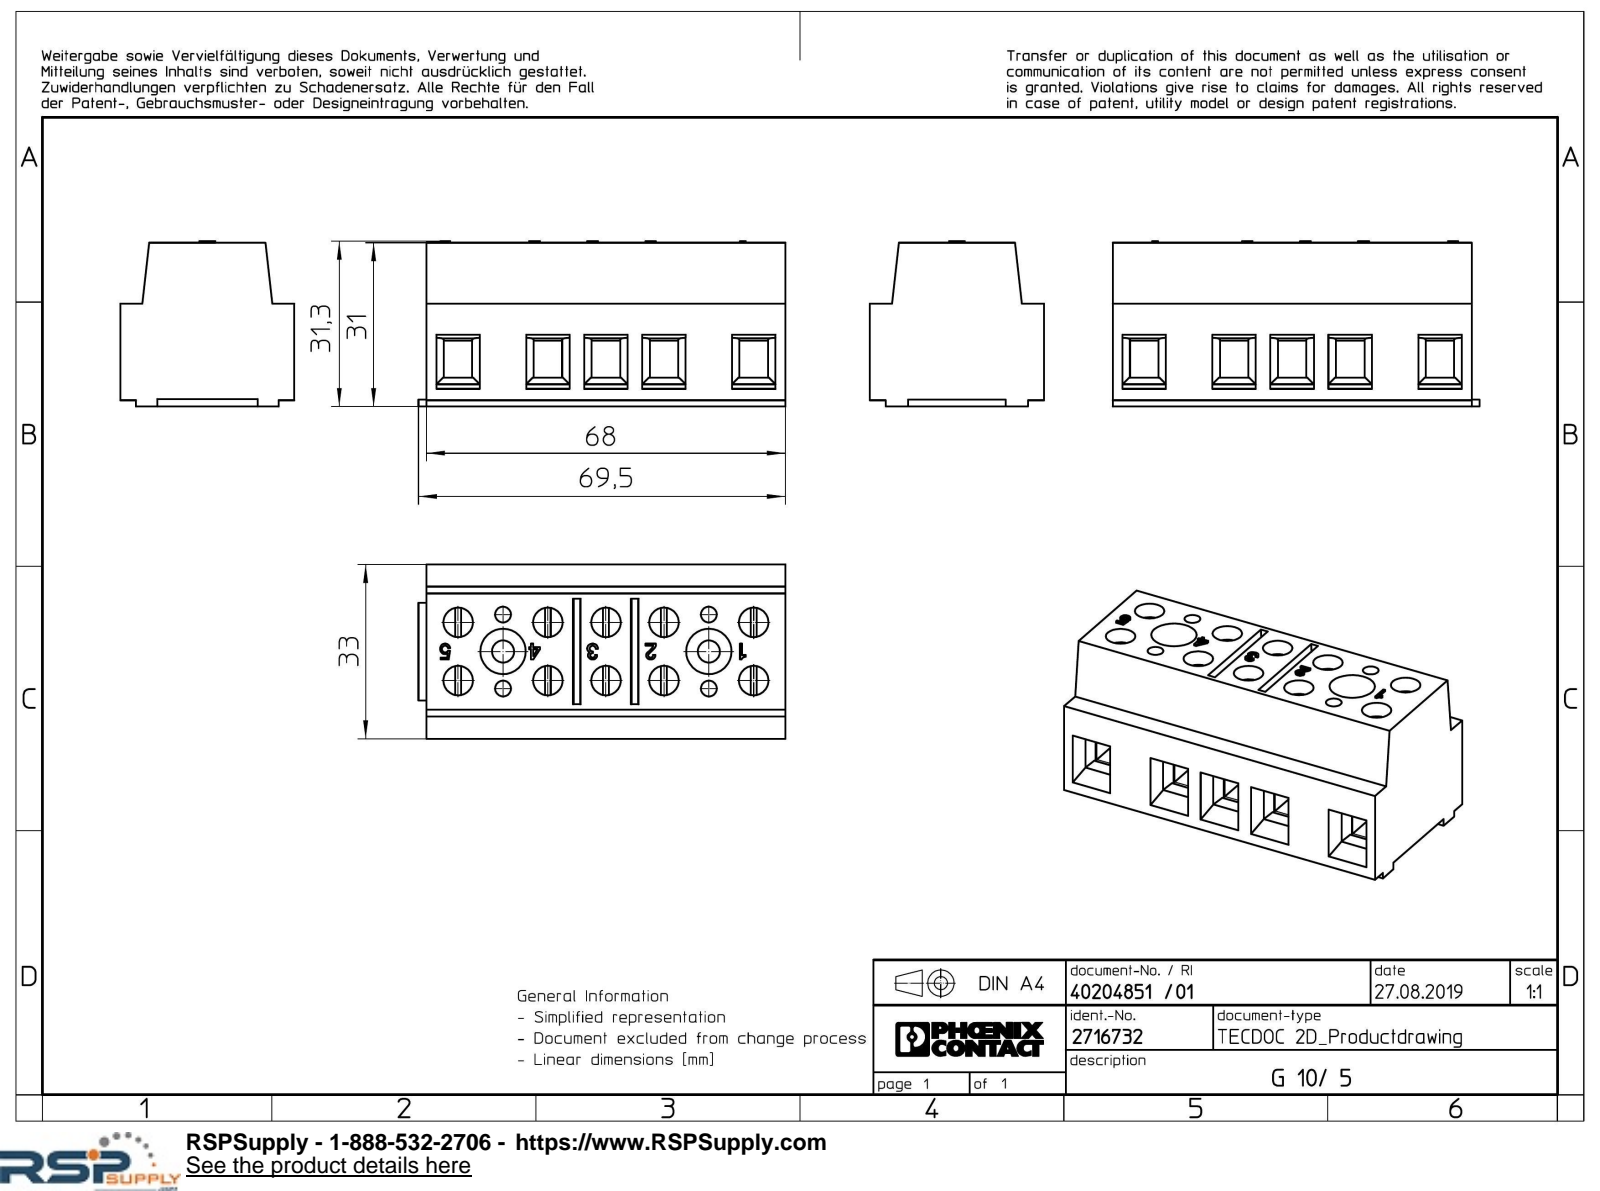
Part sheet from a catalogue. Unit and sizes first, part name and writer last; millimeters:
Units: millimetres
Overall size (bounding box): 69.5 × 33 × 31.3
Round holes (diameter × count): ⌀5.6 ×10, ⌀3 ×4, ⌀4.2 ×2, ⌀8.6 ×2
Main face-to-face distances: 31, 11, 68, 33, 39, 5.4, 28, 17, 19.5, 11.5
Hole centre spacings: 11, 8.63, 10.12, 15.12, 39, 7, 15.56, 17
Volume: 49 691 mm³ · Surface area: 17 455 mm²
Bodies: 1 solid, 479 faces (443 planar, 36 cylindrical, 0 other)
Part name (STEP PRODUCT): G_10_5-select
STEP written by: Creo Elements/Direct Modeling 20.1A 29-Sep-2018 (C) Parametric Technology GmbH (AUTOMOTIVE_DESIGN)
